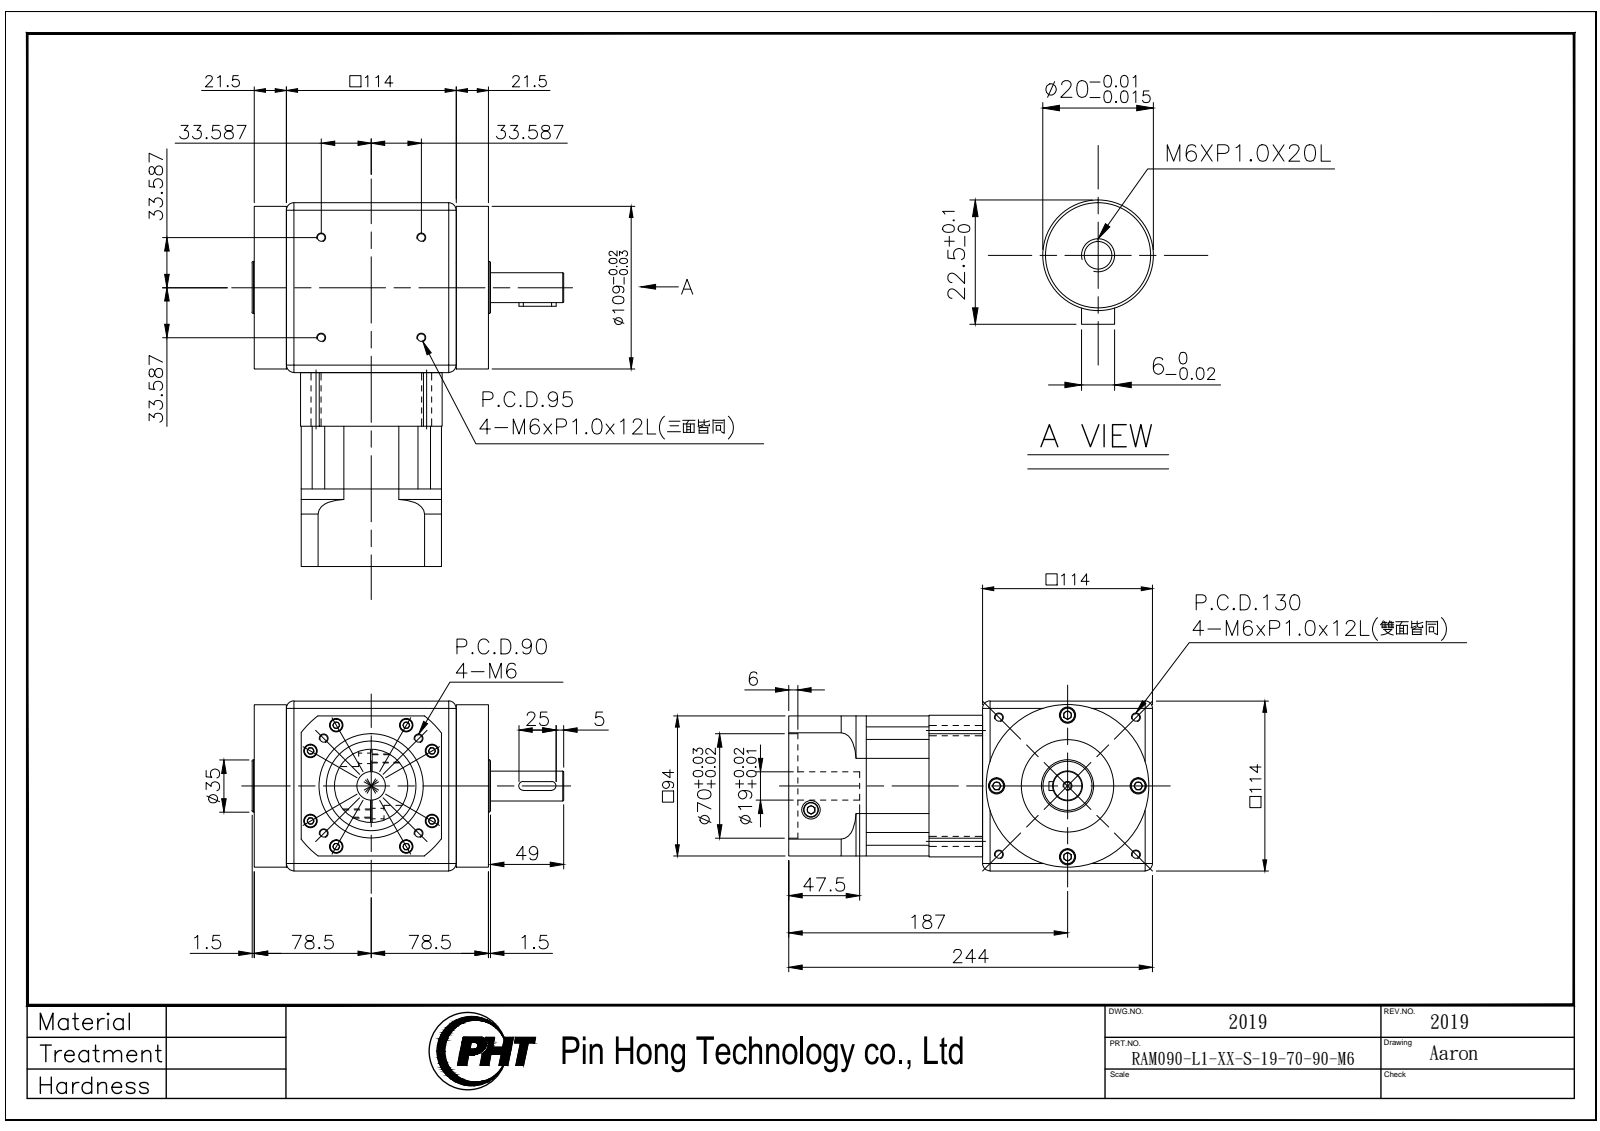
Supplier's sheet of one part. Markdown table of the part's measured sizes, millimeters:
| quantity | value |
| --- | --- |
| part name | RAM090-L1-XX-S-19-70-90-M6_2019 |
| STEP written by | SolidWorks 2016 (AUTOMOTIVE_DESIGN) |
| units | millimeters |
| bodies | 3 solids, 654 faces (295 planar, 229 cylindrical, 130 other) |
| overall size | 244 × 209 × 114 |
| volume | 2 856 000 mm³ |
| surface area | 223 947 mm² |
| round holes (diameter × count) | 5 × 17, 5.2 × 8, 9 × 8, 6.6 × 4, 6.8 × 4, 11 × 4, 12.7 × 2, 2.5 × 1, 19 × 1, 60 × 1, 70 × 1 |
| round bosses / shafts (diameter × count) | 10 × 8, 8.5 × 8, 109 × 1, 80 × 1, 62 × 1, 49 × 1, 35 × 1, 20 × 1 |
| partial cylindrical surfaces (radius × count) | 6 × 4, 3 × 2, 50.5 × 1, 59 × 1, 79.1 × 1 |
| main face-to-face distances | 114, 10, 104, 78, 192, 94, 104.5, 9.5, 0.5, 94.5 |
| hole center spacings | 47, 67.18, 12.17, 12.34, 14.08, 45.99, 47.5, 56.03 |
